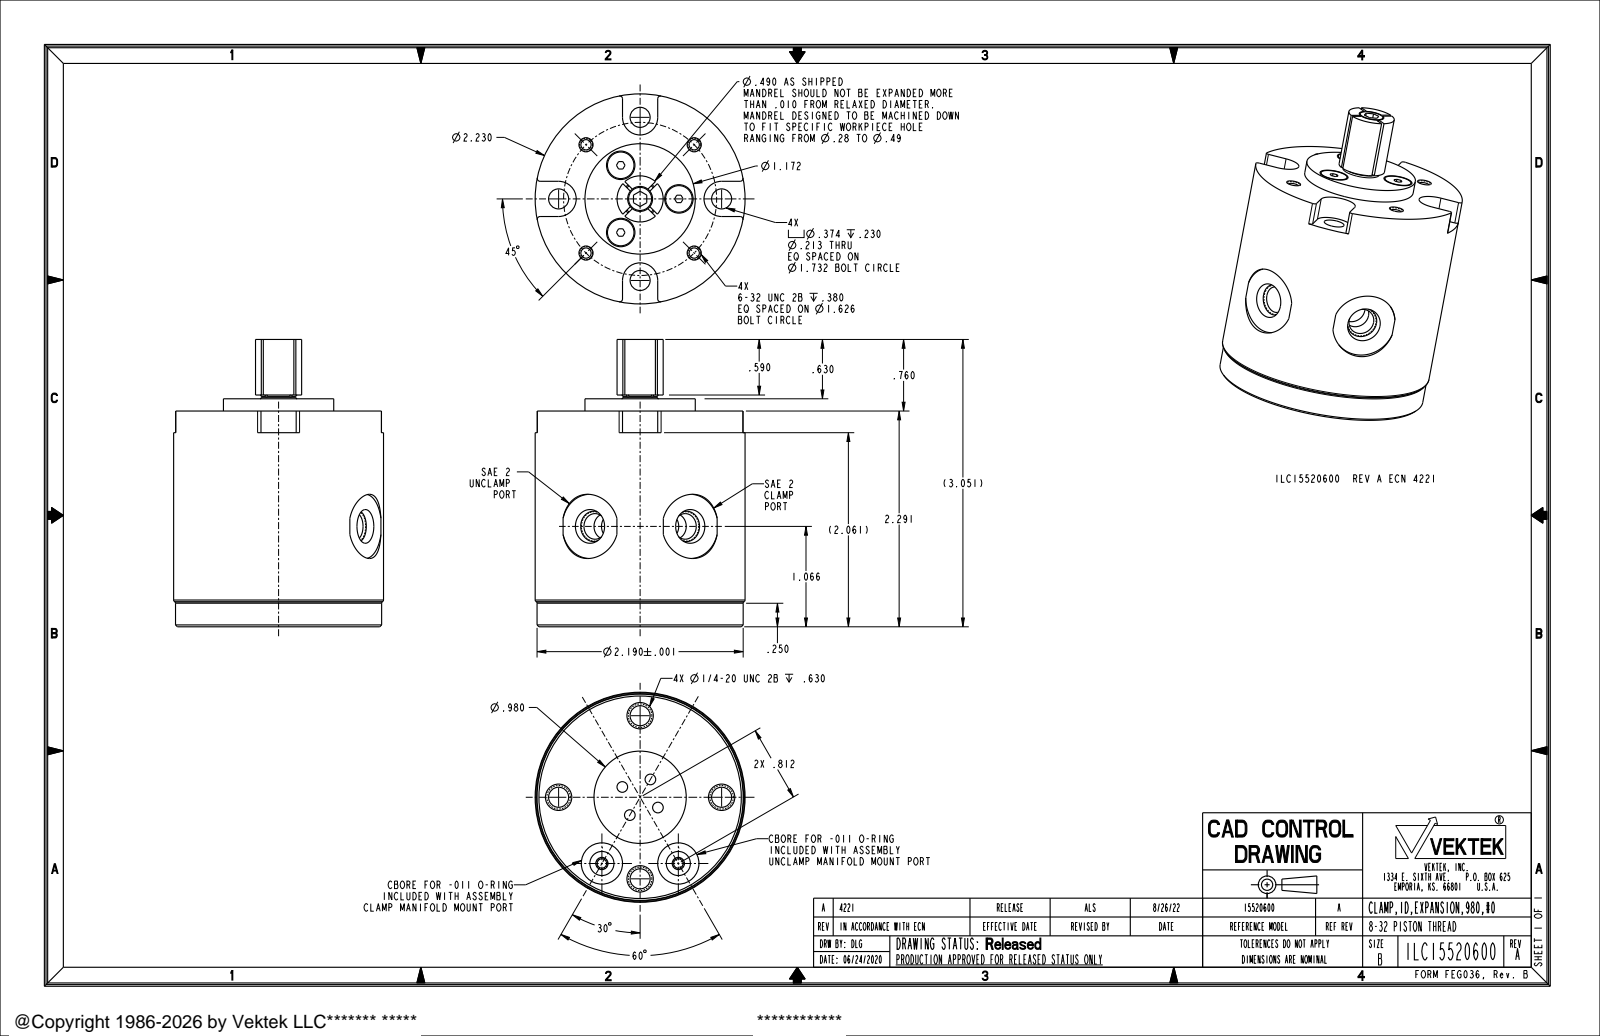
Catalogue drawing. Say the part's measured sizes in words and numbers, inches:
The part is named "ILC15520600". Its 3-D file was written by "CREO PARAMETRIC BY PTC INC, 2021164 (AUTOMOTIVE_DESIGN)". It is 1 solid with 266 faces: 96 planar, 116 cylindrical and 54 other. Overall it measures 3.051 by 2.23 by 2.23 inches. Its volume is 8.543 cubic inches and its surface area 37.91 square inches. Round holes: 4 of diameter 0.109, 4 of diameter 0.113, 4 of diameter 0.213, 3 of diameter 0.302, 2 of diameter 0.1, 2 of diameter 0.256, 2 of diameter 0.272, 2 of diameter 0.438, 2 of diameter 0.682, 1 of diameter 0.265, 1 of diameter 0.98. Round bosses or shafts: 4 of diameter 0.25, 4 of diameter 0.138, 3 of diameter 0.282, 2 of diameter 0.313, 2 of diameter 0.118, 1 of diameter 2.23, 1 of diameter 2.19, 1 of diameter 1.172. Partial cylindrical surfaces (rounded edges, fillets, slot ends): 8 of radius 0.03, 4 of radius 0.187. The main face-to-face distances are 2.291, 0.13, 2.421, 2.406, 2.276, 0.015, 0.36, 0.23, 2.046, 2.061. The hole center spacings are 0.644, 1.551, 0.219, 0.309, 0.605, 0.685, 0.78, 0.785.
